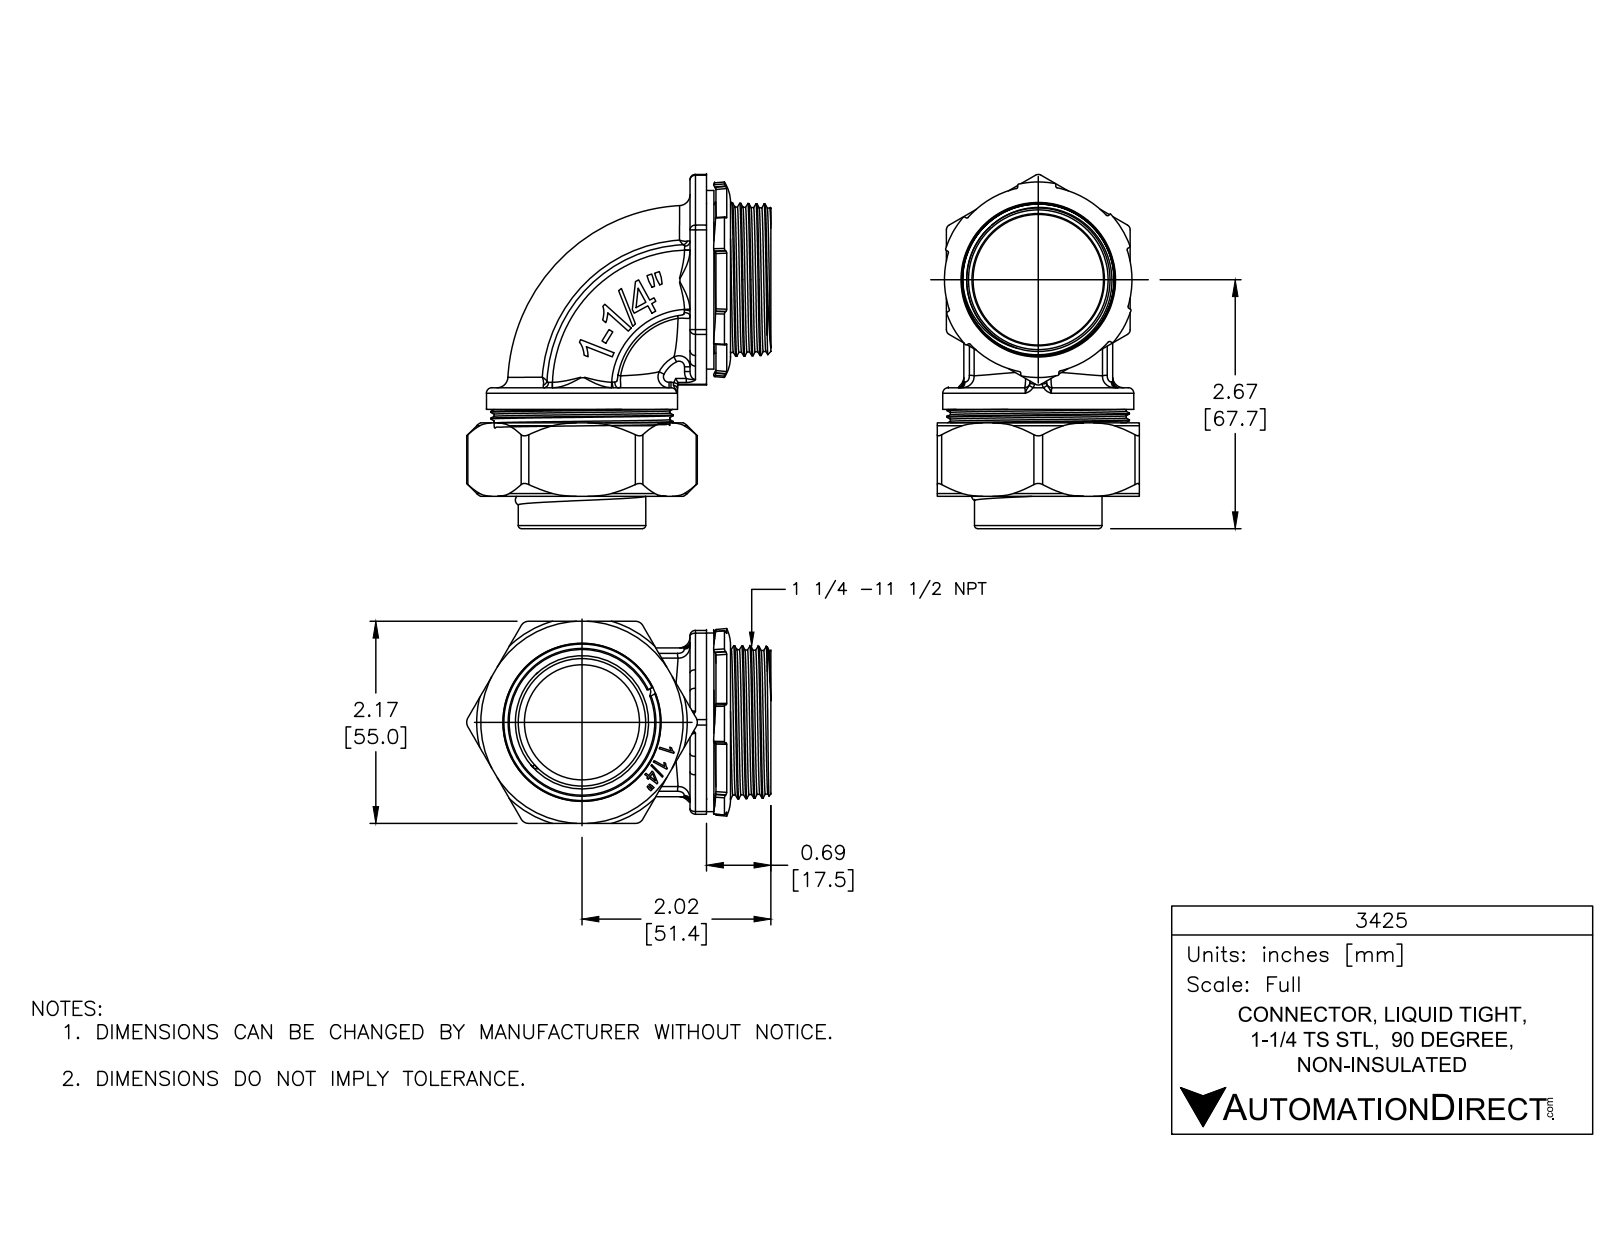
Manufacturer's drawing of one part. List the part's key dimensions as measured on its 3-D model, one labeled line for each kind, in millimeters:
Part name (STEP PRODUCT): 3425
STEP written by: SolidWorks 2018 (AUTOMOTIVE_DESIGN)
Units: millimetres
Bodies: 6 solids, 678 faces (271 planar, 123 cylindrical, 284 other)
Overall size (bounding box): 96.4 × 82.8 × 55
Volume: 60 600 mm³ · Surface area: 55 720 mm²
Round holes (diameter × count): ⌀35.5 ×2, ⌀4.6 ×1, ⌀31.3 ×1, ⌀33 ×1, ⌀36 ×1, ⌀39.5 ×1, ⌀41.6 ×1, ⌀42.3 ×1, ⌀43 ×1, ⌀44.7 ×1, ⌀48.5 ×1
Round bosses / shafts (diameter × count): ⌀52 ×1, ⌀49.6 ×1, ⌀48.6 ×1, ⌀47.5 ×1, ⌀44 ×1, ⌀34.7 ×1, ⌀33 ×1, ⌀3.8 ×1
Partial cylindrical surfaces — rounded edges, fillets, slot ends (radius × count): R1.5 ×16, R0.3 ×8, R2.4 ×6, R0.1 ×2, R1.2 ×2, R1.3 ×2, R0.2 ×1, R0.4 ×1
Main face-to-face distances: 55, 7.2, 47.8, 23.7, 40.5, 2, 20, 9.6, 50, 4.5
Hole centre spacings: 24.5
